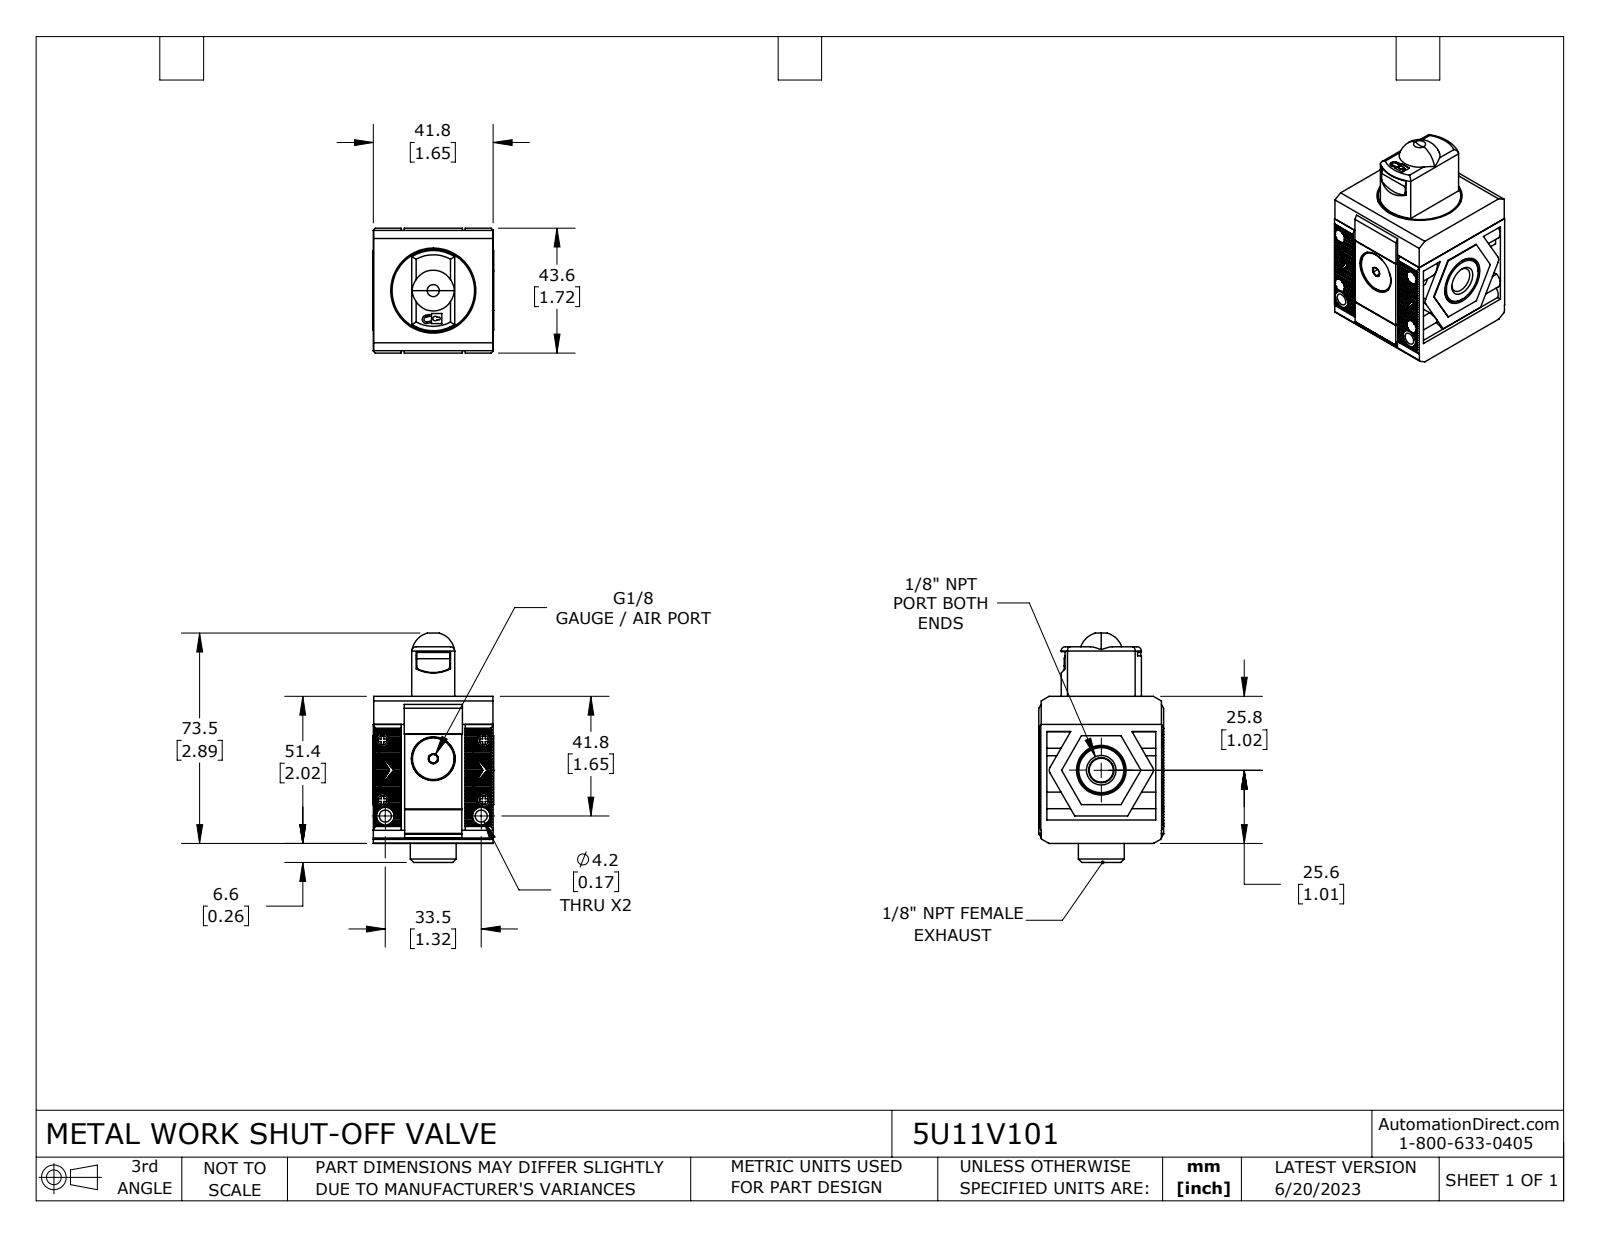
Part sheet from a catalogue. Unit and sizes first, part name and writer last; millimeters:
Units: millimetres
Overall size (bounding box): 80.1 × 43.6 × 42.2
Round holes (diameter × count): ⌀2.1 ×4, ⌀3 ×4, ⌀4.7 ×4, ⌀4.2 ×2, ⌀8.6 ×2, ⌀15.3 ×1, ⌀29.7 ×1, ⌀31.3 ×1
Round bosses / shafts (diameter × count): ⌀4.6 ×4, ⌀2.6 ×4, ⌀6.2 ×2, ⌀32 ×1, ⌀28.8 ×1, ⌀22.8 ×1, ⌀18.2 ×1, ⌀16 ×1
Partial cylindrical surfaces — rounded edges, fillets, slot ends (radius × count): R0.6 ×4, R1.5 ×4, R3.1 ×4, R0.2 ×2, R2 ×2, R0.5 ×1, R0.8 ×1, R1 ×1
Main face-to-face distances: 41.6, 34, 7.8, 41.7, 42.5, 9.8, 42, 51.4, 1.1, 0.8
Hole centre spacings: 5.6, 18.8, 20.9, 22.9, 26.1, 26.5, 34.9, 35.4
Volume: 95 600 mm³ · Surface area: 34 510 mm²
Bodies: 13 solids, 1159 faces (817 planar, 206 cylindrical, 136 other)
Part name (STEP PRODUCT): 5U11V101
STEP written by: SolidWorks 2021 (CONFIG_CONTROL_DESIGN)
